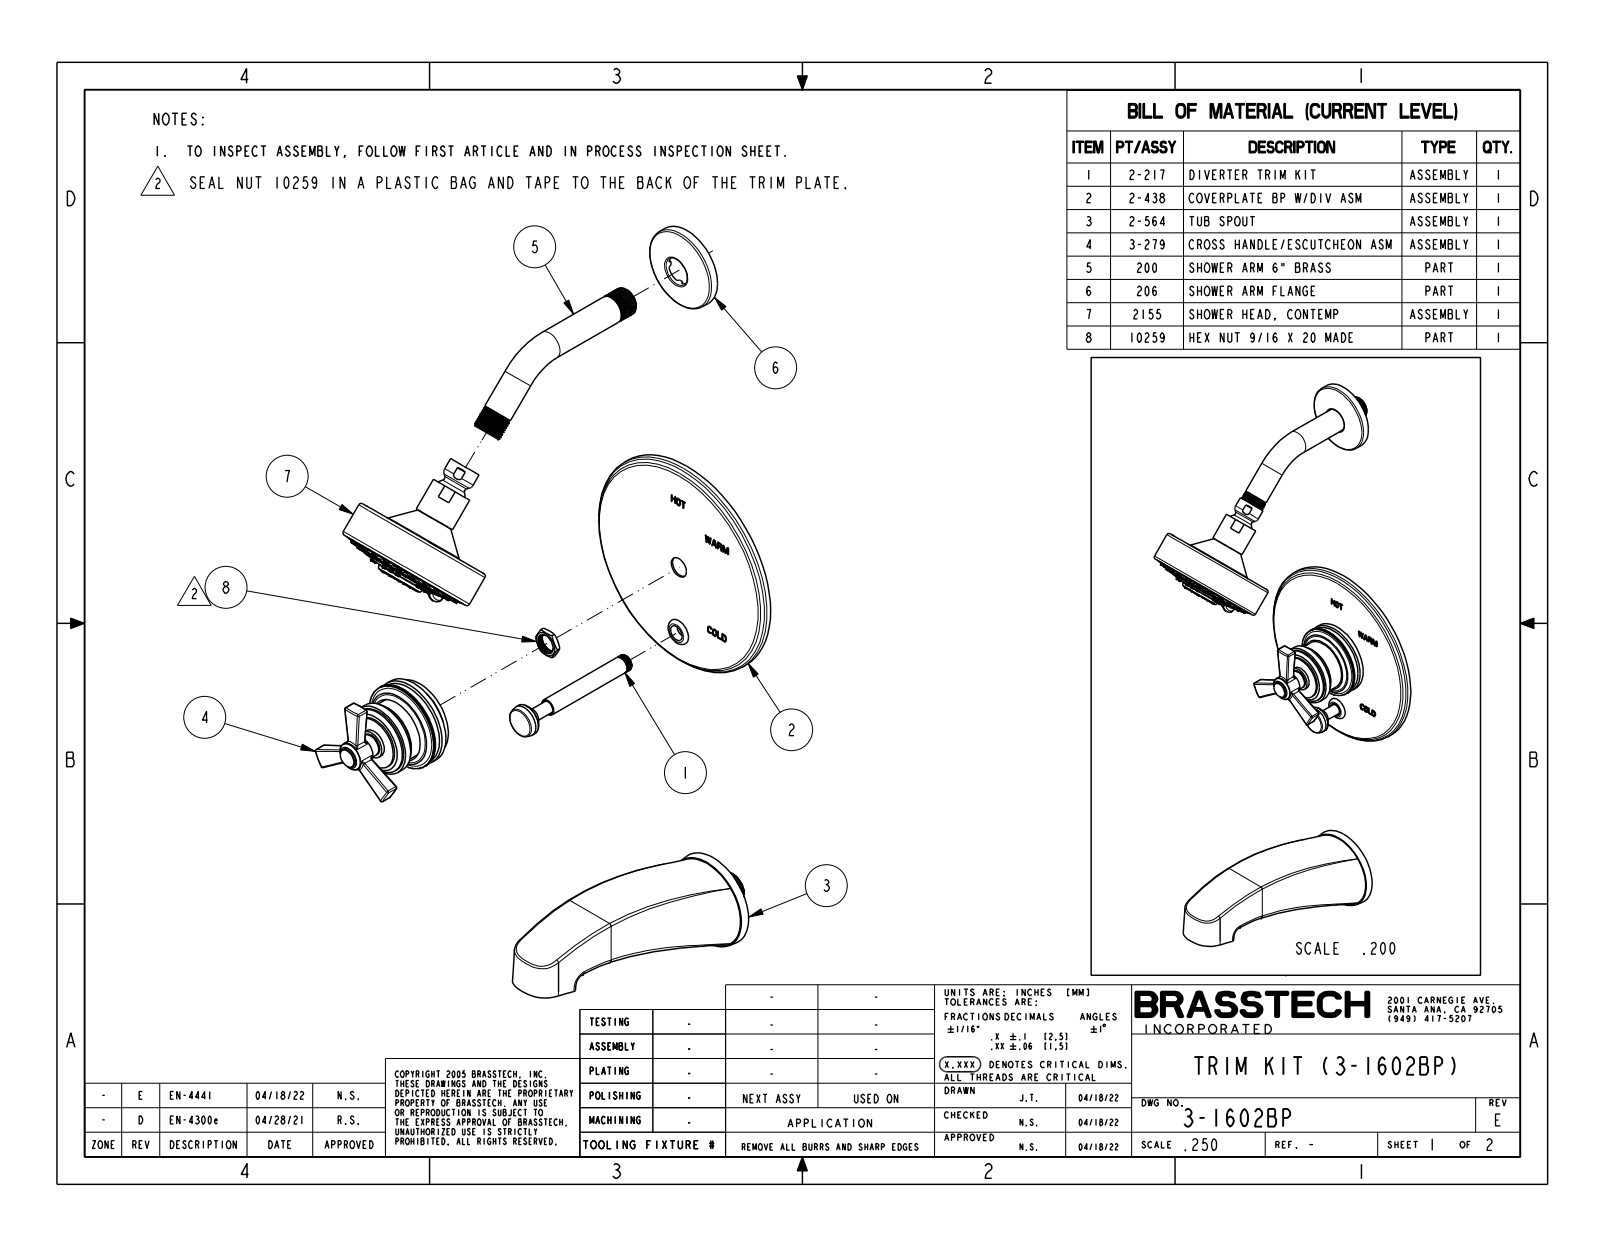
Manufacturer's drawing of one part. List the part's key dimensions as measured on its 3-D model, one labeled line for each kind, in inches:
Part name (STEP PRODUCT): 3-1602BP
STEP written by: CREO PARAMETRIC BY PTC INC, 2018400 (CONFIG_CONTROL_DESIGN)
Units: inches
Bodies: 3 solids, 2060 faces (782 planar, 414 cylindrical, 864 other)
Overall size (bounding box): 21.565 × 8.175 × 6.5
Volume: 60.54 in³ · Surface area: 224.4 in²
Round holes (diameter × count): ⌀0.059 ×8, ⌀0.925 ×1
Round bosses / shafts (diameter × count): ⌀0.142 ×39, ⌀0.165 ×23, ⌀0.813 ×2, ⌀6.5 ×1, ⌀4 ×1, ⌀3.724 ×1, ⌀2.5 ×1, ⌀2.4 ×1
Partial cylindrical surfaces — rounded edges, fillets, slot ends (radius × count): R0.079 ×8, R0.04 ×6, R0.1 ×6, R0.02 ×2, R0.138 ×1, R0.472 ×1, R0.512 ×1, R0.63 ×1
Main face-to-face distances: 0.313, 2.088, 1.775, 0.2, 0.1, 1.148, 1.3, 0.15, 0.4, 1.375
Hole centre spacings: 0.443, 0.579, 1.069, 0.819, 0.818, 1.157, 1.157
